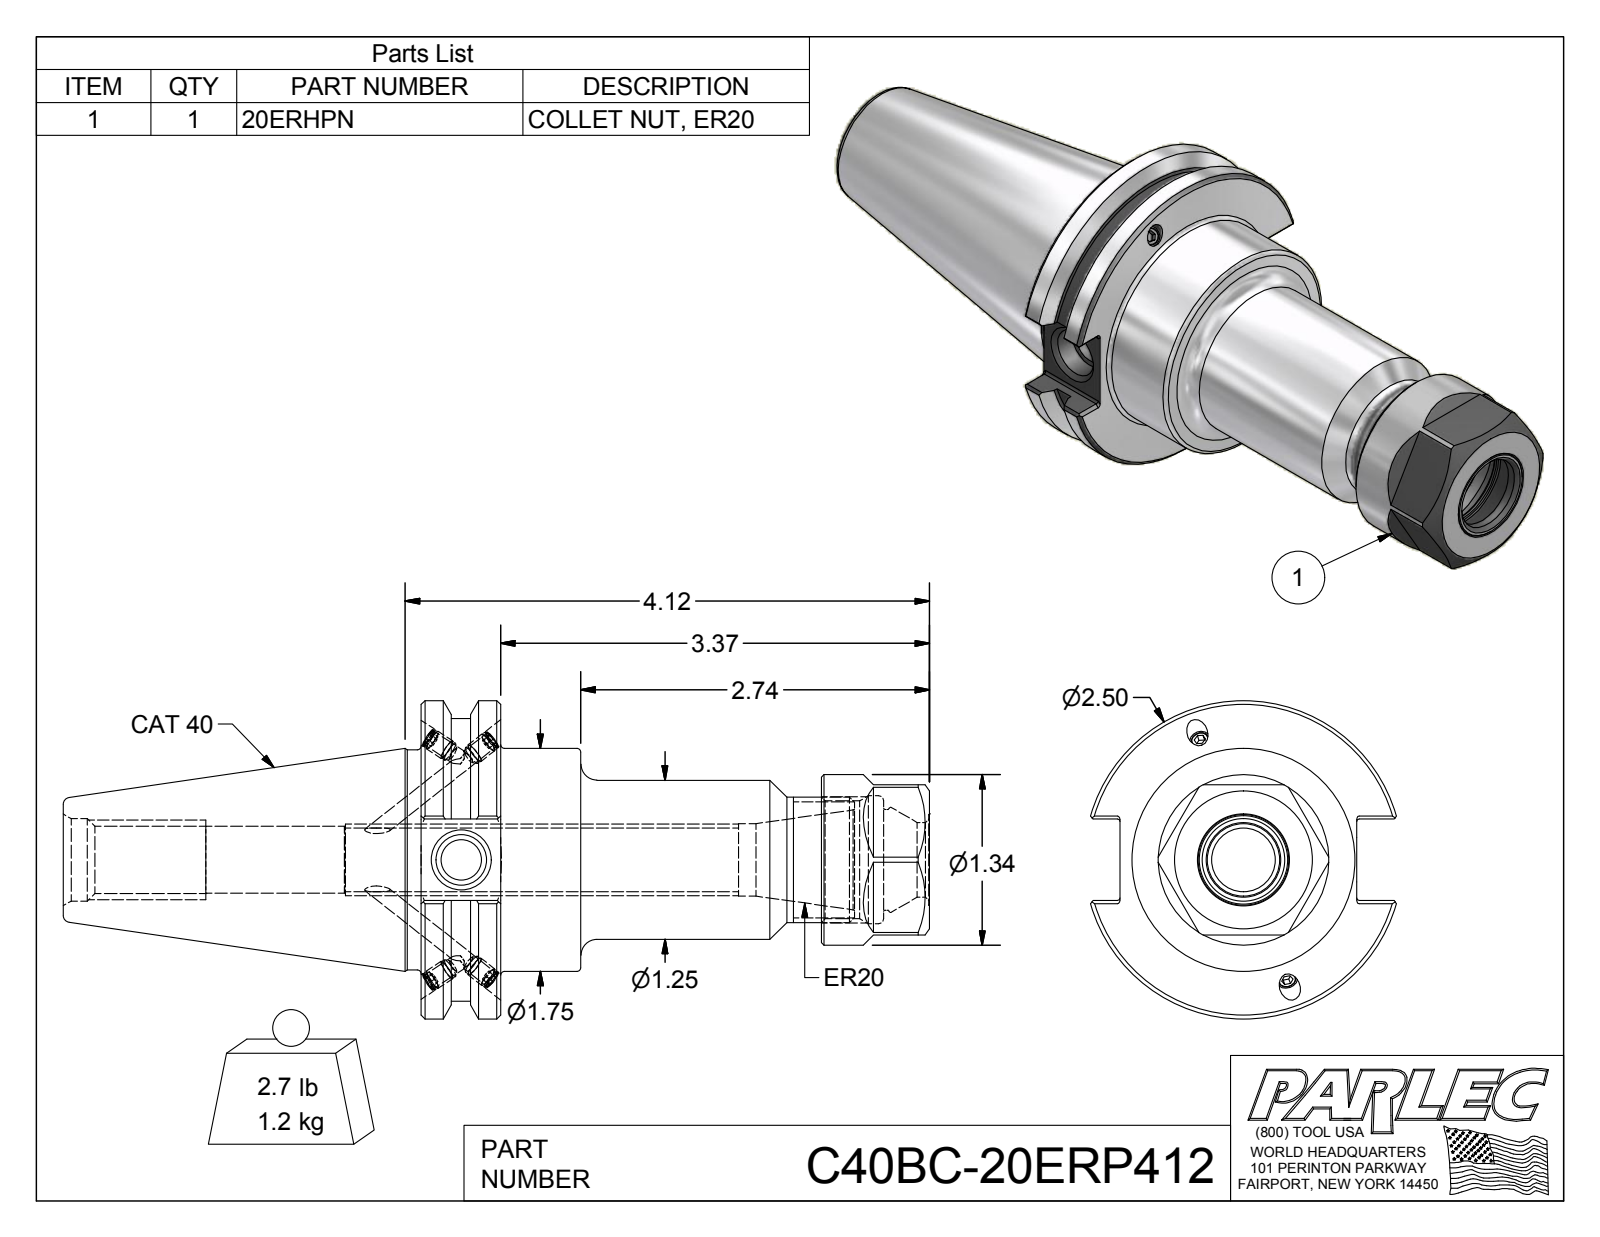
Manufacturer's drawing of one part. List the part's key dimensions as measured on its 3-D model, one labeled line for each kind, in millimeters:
Part name (STEP PRODUCT): C40BC-20ERP412; C40BCB-20ER4-1; 029-965; 20ERHPN
STEP written by: Autodesk Inventor 2012 (AUTOMOTIVE_DESIGN)
Units: millimetres
Bodies: 6 solids, 200 faces (93 planar, 54 cylindrical, 53 other)
Overall size (bounding box): 172.9 × 63.5 × 61
Volume: 162 600 mm³ · Surface area: 36 150 mm²
Round holes (diameter × count): ⌀3.3 ×4, ⌀4.1 ×4, ⌀8 ×1, ⌀10.1 ×1, ⌀12.8 ×1, ⌀13.4 ×1, ⌀13.4 ×1, ⌀14.5 ×1, ⌀14.9 ×1, ⌀16.5 ×1, ⌀20.1 ×1, ⌀23.5 ×1
Round bosses / shafts (diameter × count): ⌀4.2 ×4, ⌀4 ×4, ⌀63.5 ×1, ⌀56.4 ×1, ⌀44.5 ×1, ⌀43.9 ×1, ⌀34 ×1, ⌀31.8 ×1
Partial cylindrical surfaces — rounded edges, fillets, slot ends (radius × count): R0.5 ×12
Main face-to-face distances: 15.9, 30, 79.9, 64, 101.5, 85.6, 21.6, 31.9, 16, 48
